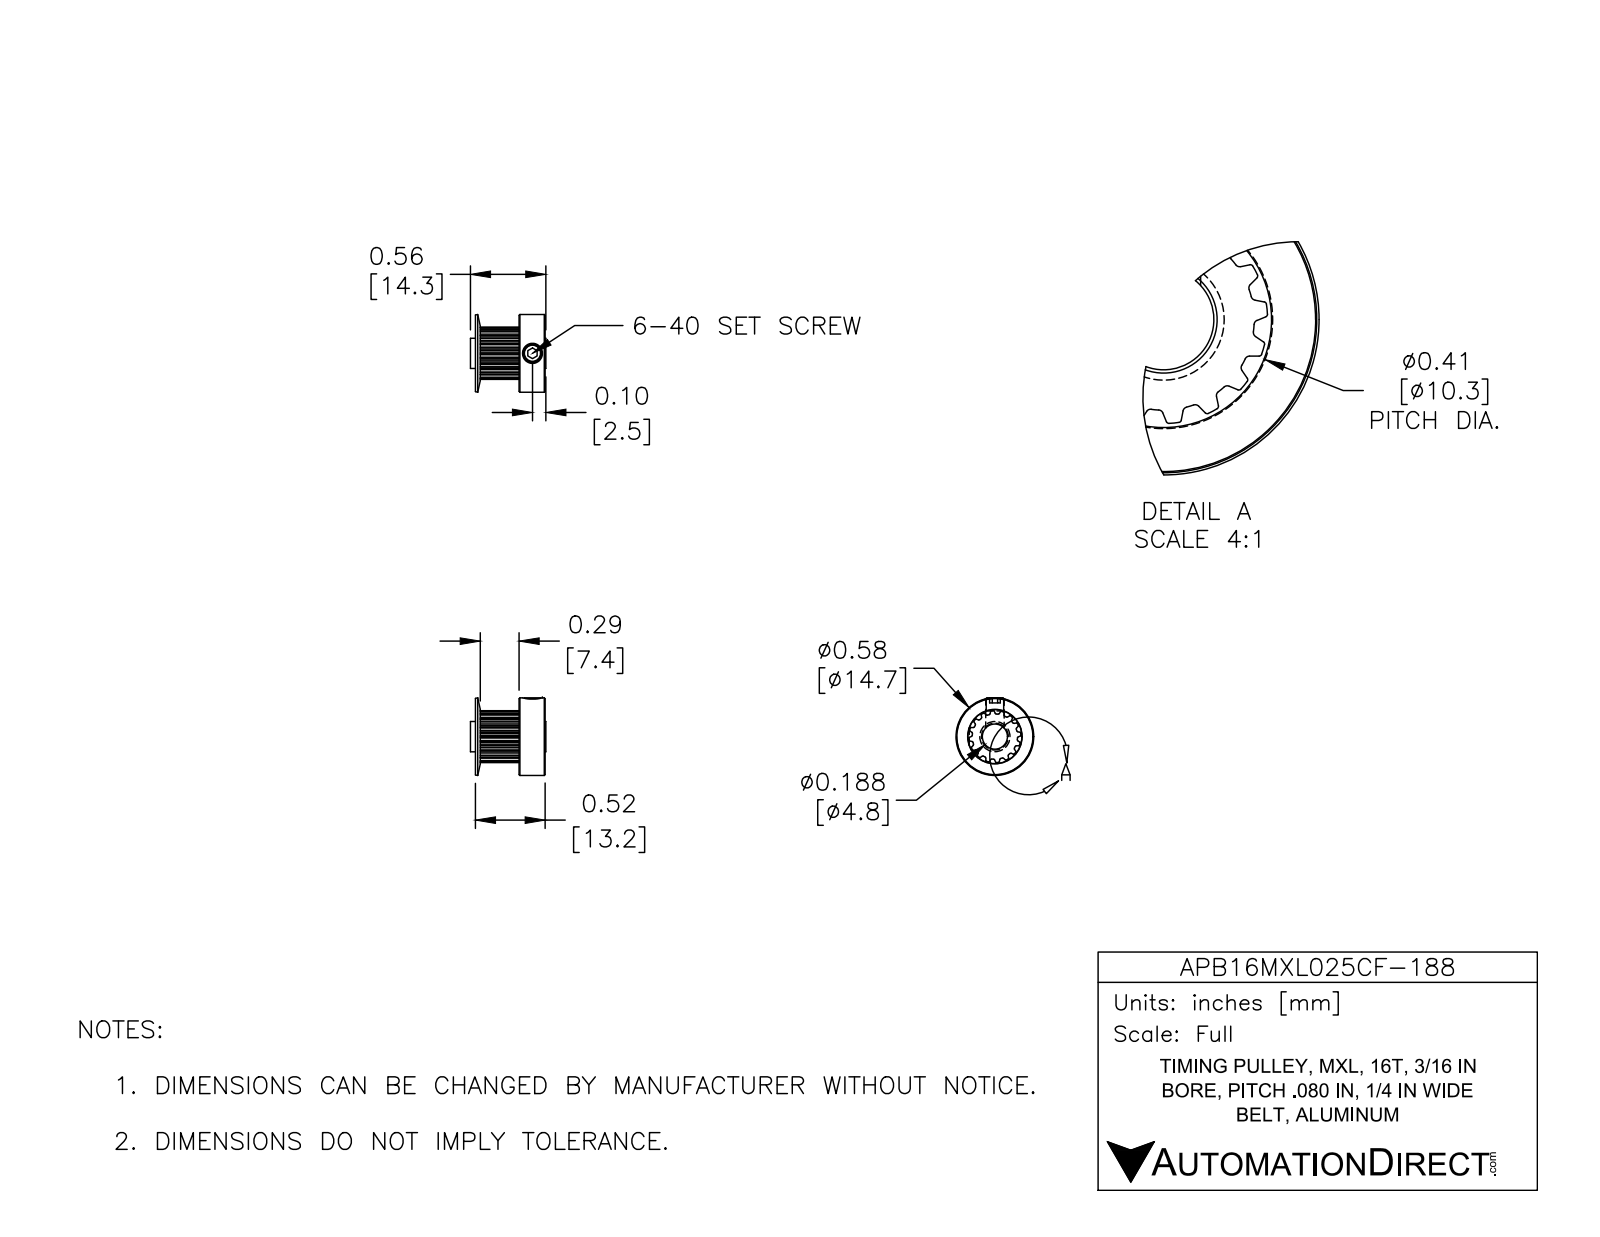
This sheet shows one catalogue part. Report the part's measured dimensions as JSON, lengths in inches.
{"part_name": "APB16MXL025CF-188", "step_written_by": "SolidWorks 2016 (AUTOMOTIVE_DESIGN)", "units": "inches", "bodies": {"solids": 2, "faces": 184, "planar": 47, "cylindrical": 119, "other": 18}, "overall_size": [0.58, 0.58, 0.563], "volume_in3": 0.071, "surface_area_in2": 2.132, "round_holes": [[0.138, 1], [0.187, 1]], "round_bosses_or_shafts": [[0.58, 1], [0.226, 1], [0.13, 1]], "partial_cylinders_radius": [[0.005, 32], [0.009, 32], [0.169, 1], [0.194, 1]], "face_to_face_distances": [0.194, 0.309, 0.504, 0.136, 0.019, 0.29, 0.485, 0.508, 0.489, 0.199]}
